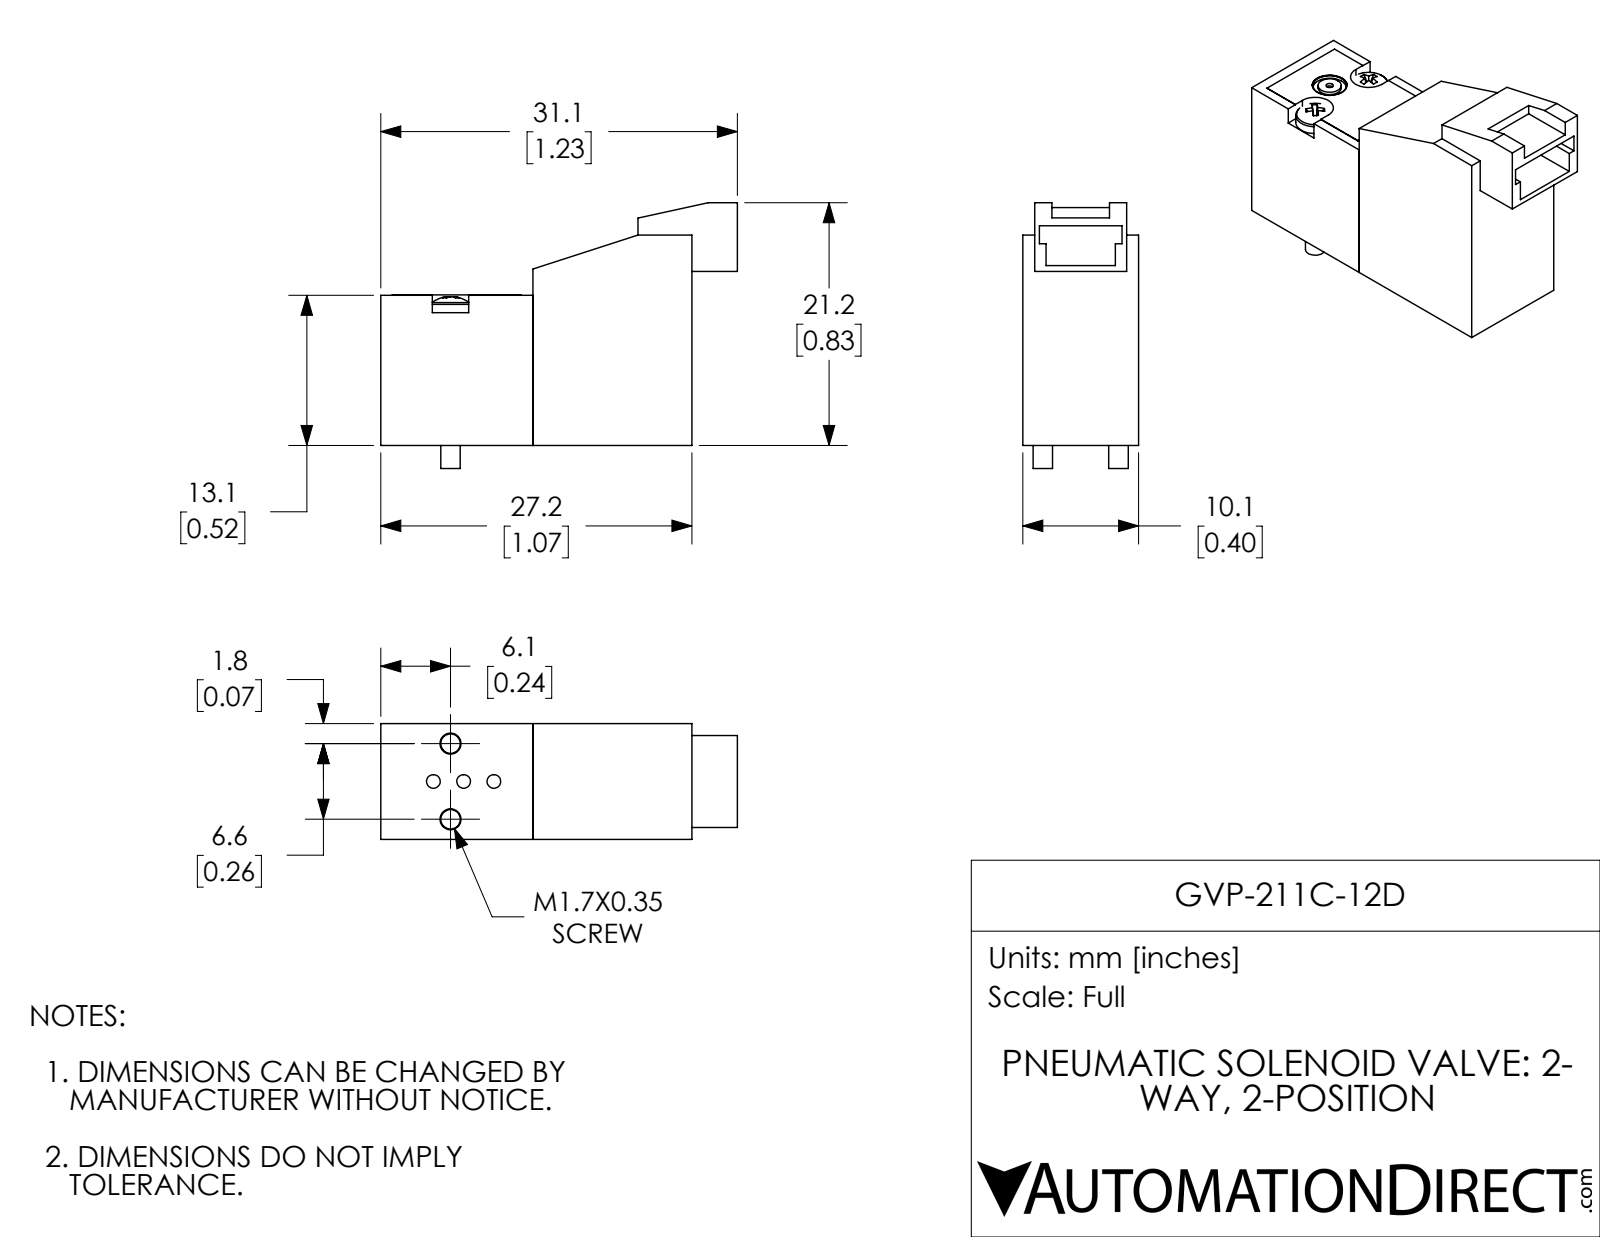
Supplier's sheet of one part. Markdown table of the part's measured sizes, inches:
| quantity | value |
| --- | --- |
| part name | GVP-211C-12D |
| STEP written by | SolidWorks 2018 (AUTOMOTIVE_DESIGN) |
| units | inches |
| bodies | 4 solids, 126 faces (83 planar, 29 cylindrical, 14 other) |
| overall size | 1.226 × 0.913 × 0.398 |
| volume | 0.259 in³ |
| surface area | 4.199 in² |
| round holes (diameter × count) | 0.047 × 3, 0.072 × 2, 0.025 × 1, 0.115 × 1, 0.12 × 1 |
| round bosses / shafts (diameter × count) | 0.134 × 2, 0.067 × 2, 0.08 × 1 |
| partial cylindrical surfaces (radius × count) | 0.062 × 2 |
| main face-to-face distances | 0.398, 0.547, 1.07, 0.523, 0.517, 0.238, 0.041, 0.357, 0.755, 0.618 |
| hole center spacings | 0.104, 0.198, 0.105, 0.137, 0.138, 0.143, 0.143, 0.143 |
